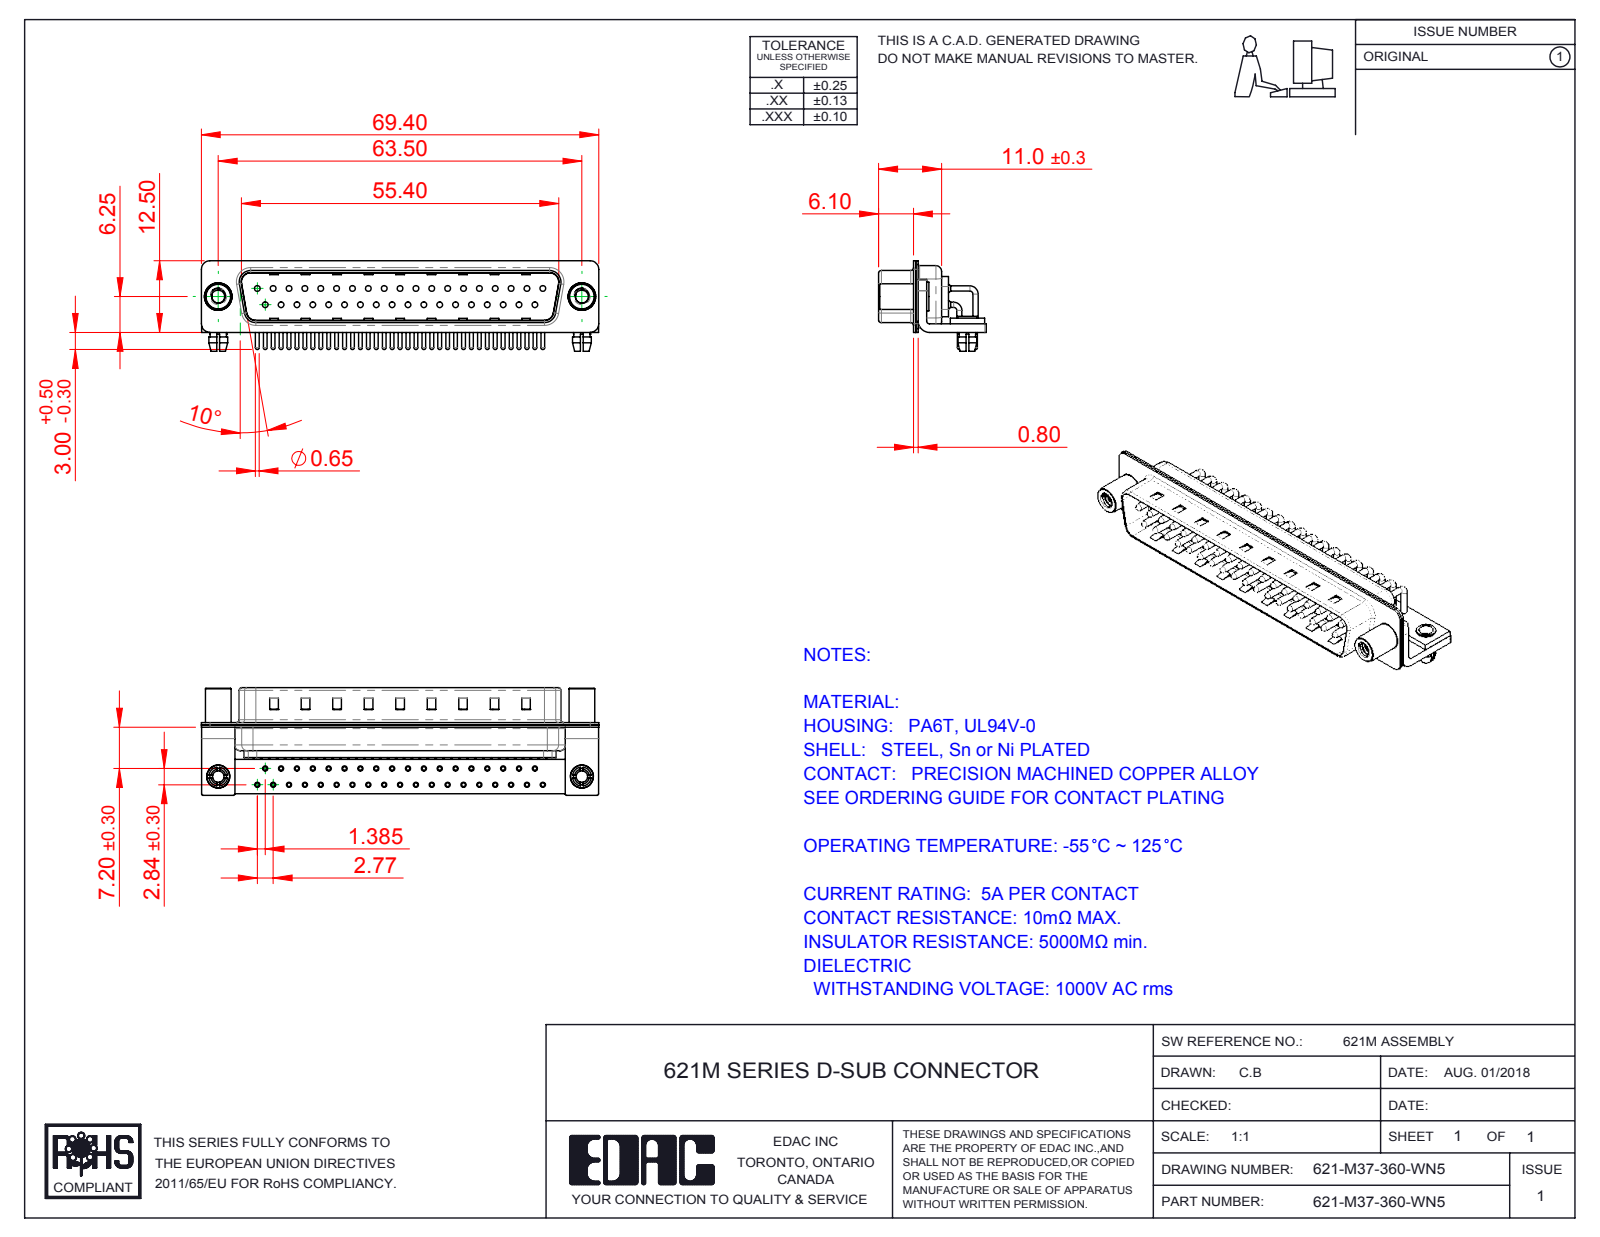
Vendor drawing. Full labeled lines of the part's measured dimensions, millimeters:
Part name (STEP PRODUCT): 621M Contact Row 2; 621-M37-360-WN5; 621M Contact Row 1; 621M Shell Front_37 Contacts (+6 more)
STEP written by: SolidWorks 2016 (CONFIG_CONTROL_DESIGN)
Units: millimetres
Bodies: 47 solids, 4748 faces (2647 planar, 1643 cylindrical, 458 other)
Overall size (bounding box): 69.4 × 18.8 × 15.8
Volume: 4 770 mm³ · Surface area: 12 476 mm²
Round holes (diameter × count): ⌀2 ×39, ⌀0.9 ×37, ⌀1 ×37, ⌀1.7 ×37, ⌀2.26 ×2, ⌀2.5 ×2, ⌀3.2 ×2, ⌀4 ×2, ⌀4.8 ×2
Round bosses / shafts (diameter × count): ⌀0.9 ×46, ⌀1.5 ×37, ⌀0.65 ×37, ⌀5 ×2, ⌀4.9 ×2, ⌀4.5 ×2, ⌀4 ×2, ⌀3.4 ×2
Partial cylindrical surfaces — rounded edges, fillets, slot ends (radius × count): R1.01 ×37, R0.25 ×16, R1.5 ×16, R2 ×13, R0.5 ×9, R1.6 ×8, R0.6 ×4, R0.65 ×4
Main face-to-face distances: 0.4, 0.85, 1.25, 9.55, 1.5, 10.4, 8.3, 0.8, 8.7, 1
Hole centre spacings: 3.16, 2.77, 5.54, 8.31, 11.08, 13.85, 5.03, 16.62
